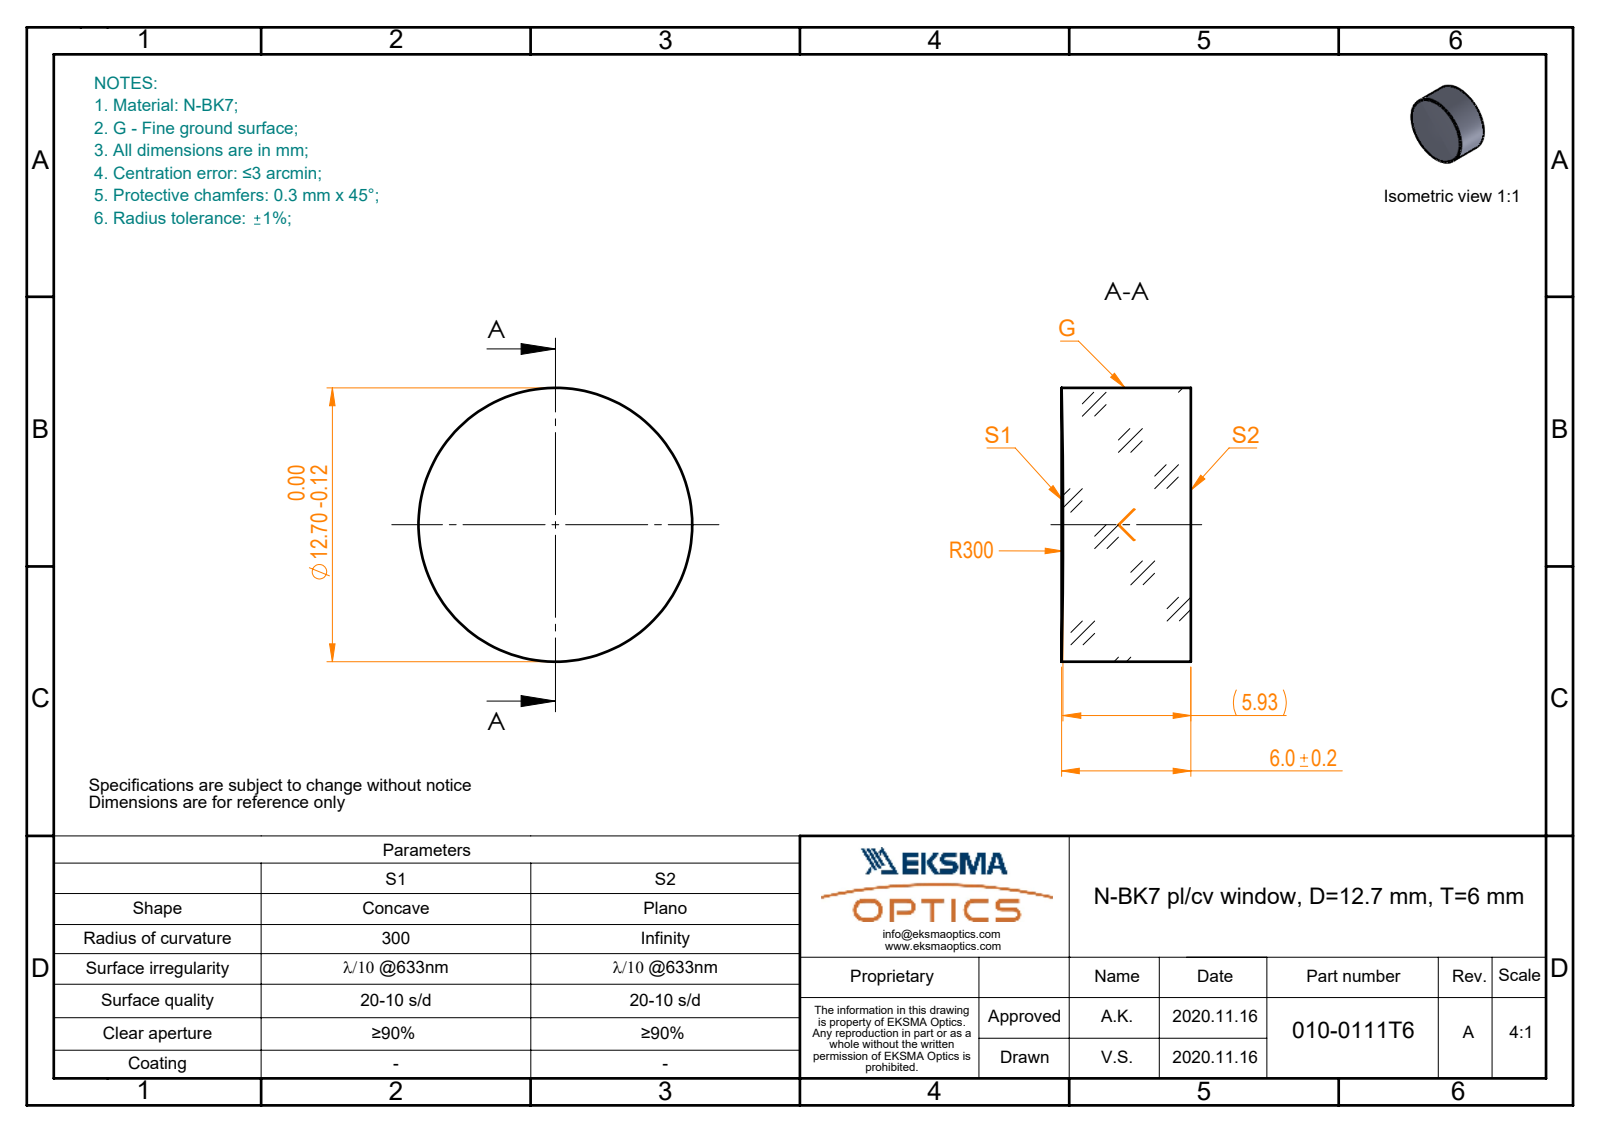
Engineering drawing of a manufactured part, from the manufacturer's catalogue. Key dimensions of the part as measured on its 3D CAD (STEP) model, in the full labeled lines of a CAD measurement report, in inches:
Part name (STEP PRODUCT): 010-0111T6_N-BK7_PCV_window
STEP written by: SolidWorks 2019 (CONFIG_CONTROL_DESIGN)
Units: inches
Bodies: 1 solid, 5 faces (1 planar, 2 cylindrical, 2 other)
Overall size (bounding box): 0.5 × 0.5 × 0.236
Volume: 0.046 in³ · Surface area: 0.764 in²
Round bosses / shafts (diameter × count): ⌀0.5 ×1
